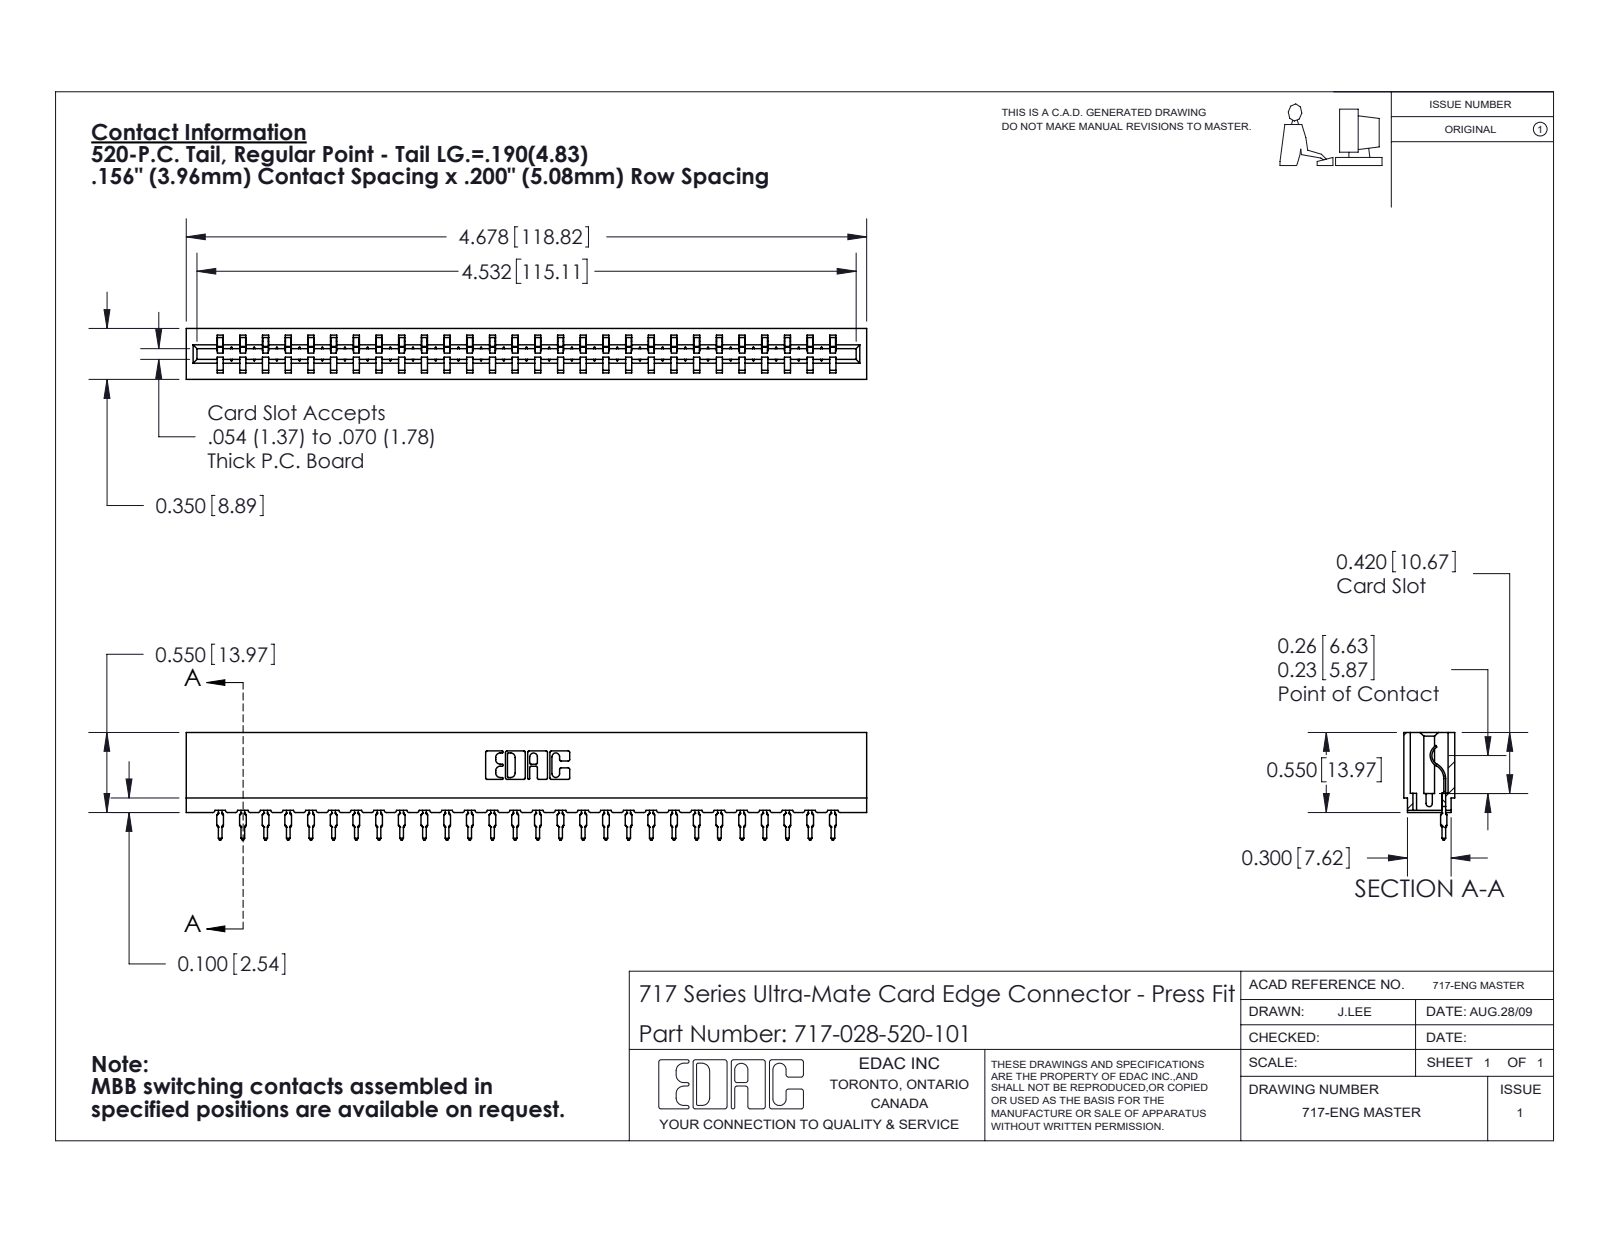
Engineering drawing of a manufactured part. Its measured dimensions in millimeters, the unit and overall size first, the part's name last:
Units: millimetres
Overall size (bounding box): 118.8 × 18.8 × 8.9
Partial cylindrical surfaces — rounded edges, fillets, slot ends (radius × count): R0.4 ×56, R0.5 ×56, R0.3 ×22, R0.2 ×6, R0.8 ×6, R0.1 ×4, R0.3 ×4, R0.7 ×3
Main face-to-face distances: 5.4, 3.5, 8.9, 1.9, 4, 1.1, 7.7, 2.4, 4.2, 0.6
Volume: 10 100 mm³ · Surface area: 13 770 mm²
Bodies: 29 solids, 3258 faces (1958 planar, 572 cylindrical, 728 other)
Part name (STEP PRODUCT): 717 Part_Insulator Option - 06; 717-028-520-101; 745-292-001_520
STEP written by: SolidWorks 2020 (CONFIG_CONTROL_DESIGN)
